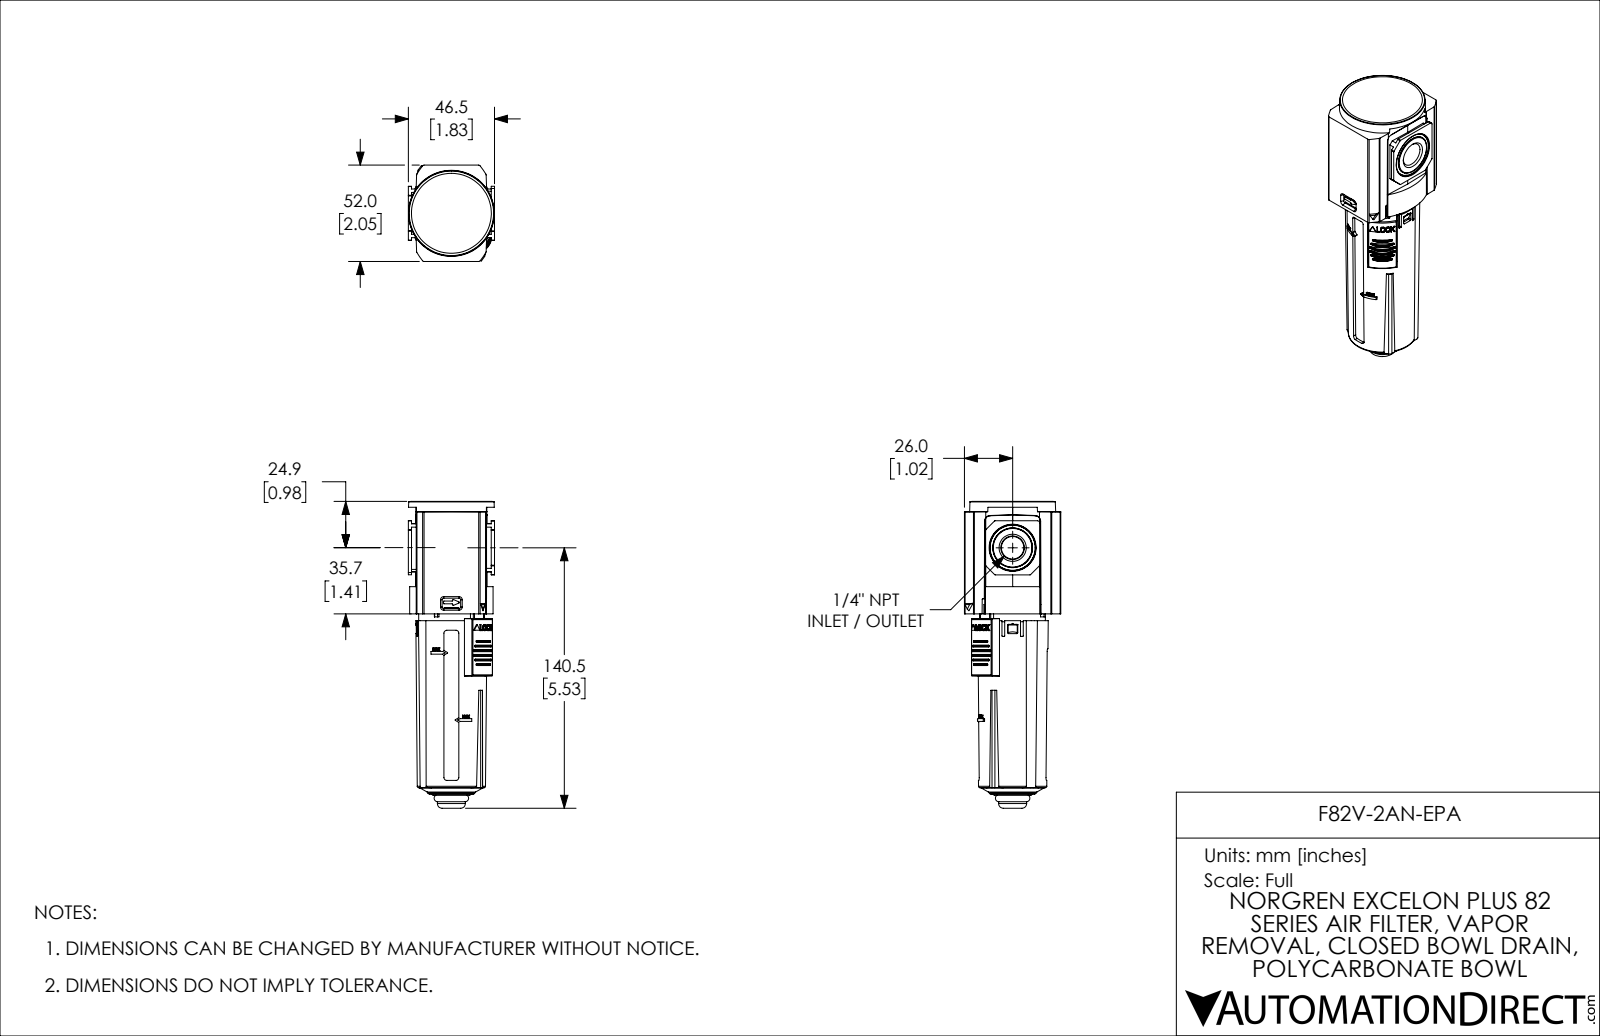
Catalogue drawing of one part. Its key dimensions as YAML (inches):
part_name: "F82V-2AN-EPA"
step_written_by: "SolidWorks 2021 (CONFIG_CONTROL_DESIGN)"
units: inches
bodies: {solids: 5, faces: 1034, planar: 457, cylindrical: 381, other: 196}
overall_size: [6.515, 2.047, 1.831]
volume: 13.24
surface_area: 87.36
round_holes:
  - {diameter: 0.059, count: 2}
  - {diameter: 0.128, count: 2}
  - {diameter: 0.63, count: 1}
round_bosses_or_shafts:
  - {diameter: 1.388, count: 1}
  - {diameter: 1.356, count: 1}
  - {diameter: 1.291, count: 1}
  - {diameter: 1.257, count: 1}
  - {diameter: 0.906, count: 1}
  - {diameter: 0.626, count: 1}
  - {diameter: 0.594, count: 1}
partial_cylinders:
  - {radius: 0.02, count: 58}
  - {radius: 0.039, count: 30}
  - {radius: 0.012, count: 11}
  - {radius: 0.008, count: 10}
  - {radius: 0.01, count: 10}
  - {radius: 0.031, count: 8}
  - {radius: 0.036, count: 8}
  - {radius: 0.048, count: 8}
face_to_face_distances: [0.059, 1.988, 2.047, 1.929, 0.058, 2.093, 2.151, 0.182, 0.236, 1.352]
hole_center_spacings: [0.797, 0.531, 0.594, 1.063, 1.189]
